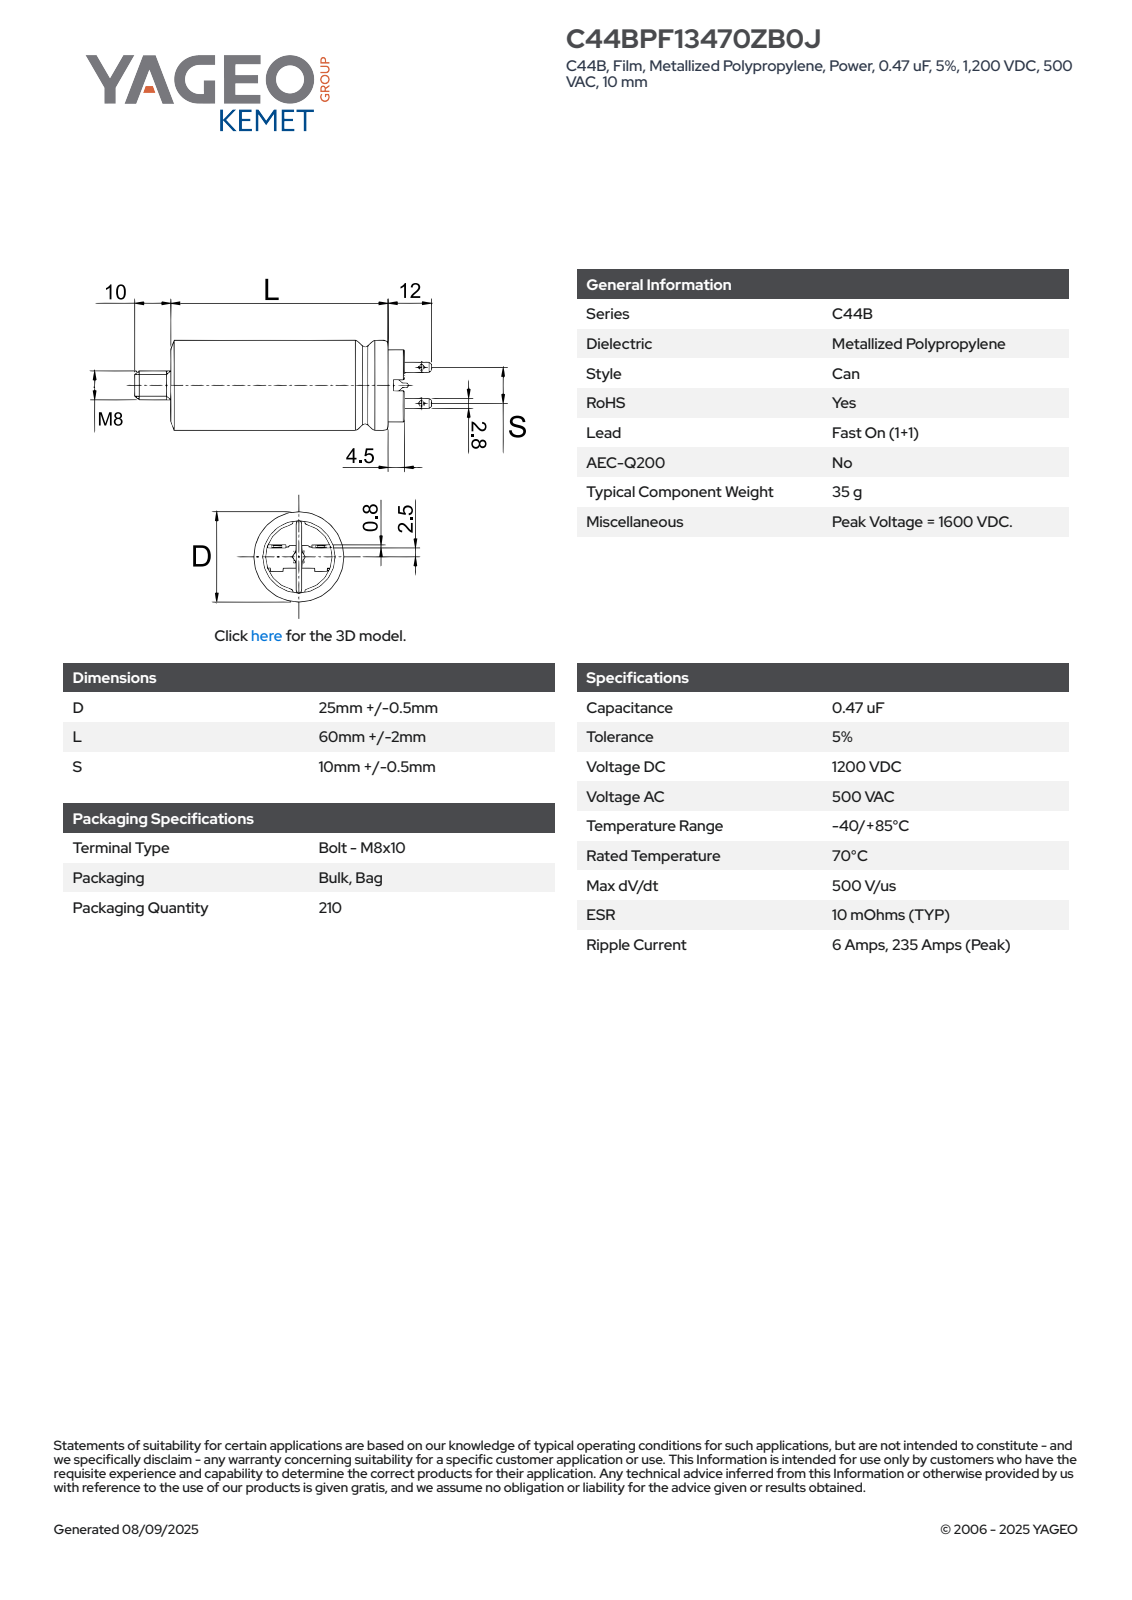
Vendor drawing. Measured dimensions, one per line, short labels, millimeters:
name: CFP_C44B_25X60_D25.5L62S10.5
written by: SolidWorks 2014 (AUTOMOTIVE_DESIGN)
unit: mm
bodies: 1 solid, 132 faces (49 planar, 40 cylindrical, 43 other)
size: 84 × 25.5 × 25.5
volume: 32 259 mm³; area: 7 048 mm²
bosses: 1× ⌀25.5, 1× ⌀20.18, 1× ⌀18.18, 1× ⌀8
rounds: 6× R0.2, 1× R0.68, 1× R12.74
face distances: 62, 0.8, 66.5, 4.5, 10, 72, 76.5, 2.8, 10.5, 2.25
